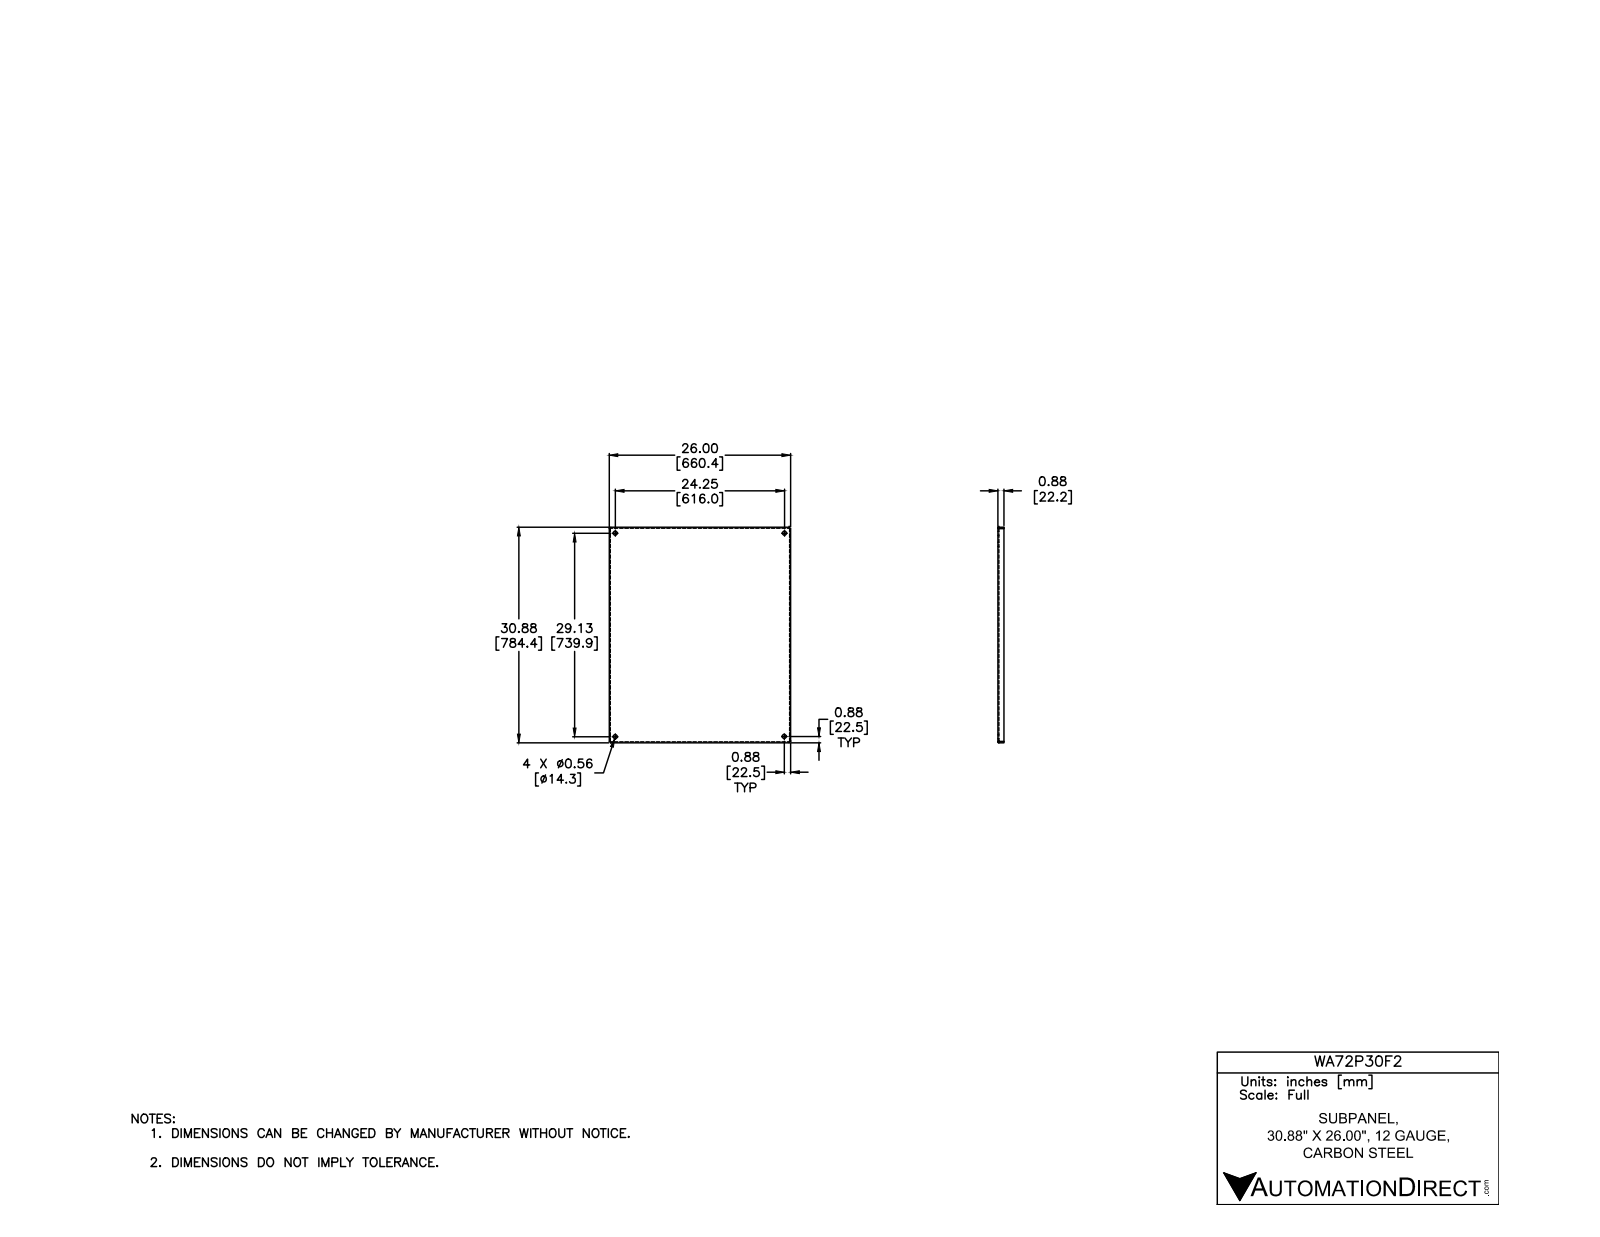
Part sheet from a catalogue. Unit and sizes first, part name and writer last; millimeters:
Units: millimetres
Overall size (bounding box): 784.4 × 660.4 × 22.2
Round holes (diameter × count): ⌀14.3 ×4
Partial cylindrical surfaces — rounded edges, fillets, slot ends (radius × count): R0.8 ×4, R3.2 ×4
Main face-to-face distances: 2.4, 658, 782, 655.7, 660.4, 784.4, 779.6, 19.8, 22.2, 4.1
Hole centre spacings: 616, 739.9, 739.9, 962.7, 962.7
Volume: 1 361 000 mm³ · Surface area: 1 151 000 mm²
Bodies: 1 solid, 42 faces (22 planar, 12 cylindrical, 8 other)
Part name (STEP PRODUCT): WA_P_F
STEP written by: Autodesk Inventor 2012 (AUTOMOTIVE_DESIGN)
